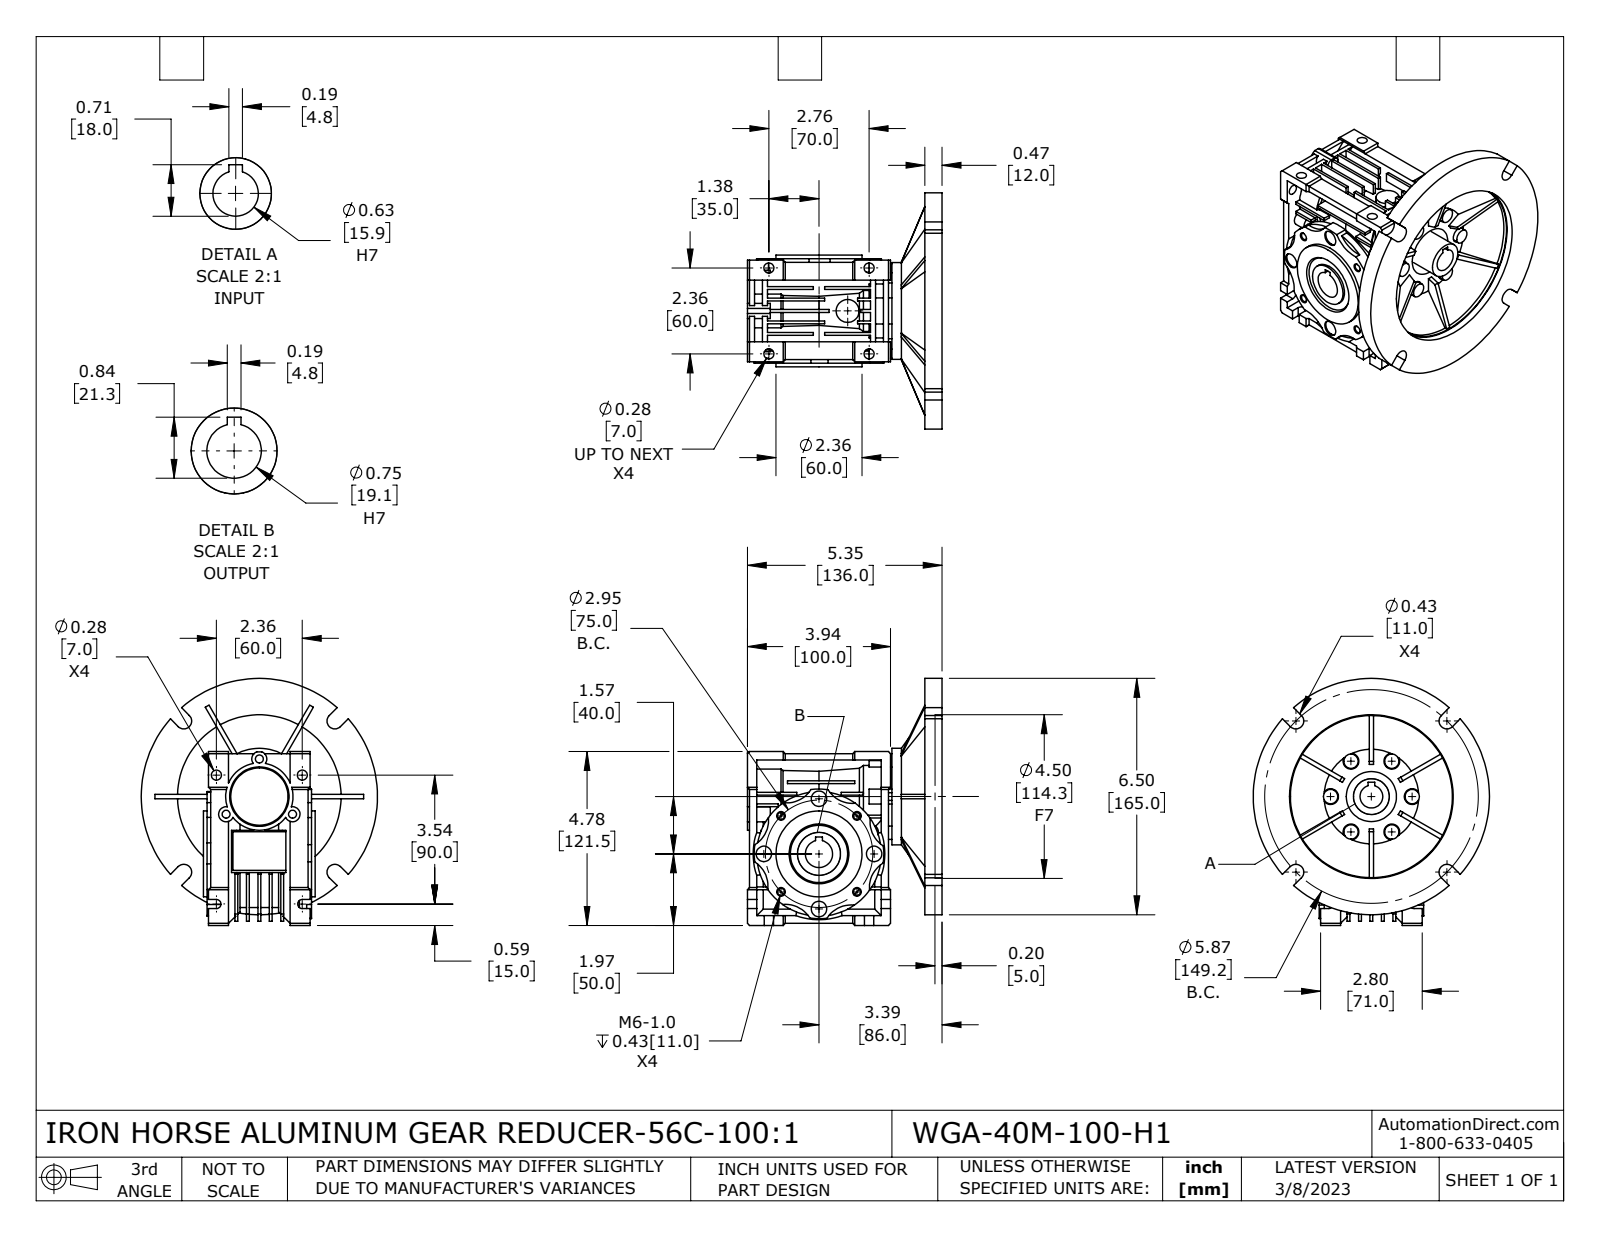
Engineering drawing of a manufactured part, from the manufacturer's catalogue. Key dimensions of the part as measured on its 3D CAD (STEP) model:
Part name (STEP PRODUCT): WGA-40M-100-H1
STEP written by: SolidWorks 2021 (CONFIG_CONTROL_DESIGN)
Units: inches
Bodies: 4 solids, 856 faces (511 planar, 251 cylindrical, 94 other)
Overall size (bounding box): 6.791 × 6.496 × 5.354
Volume: 50.34 in³ · Surface area: 315 in²
Round holes (diameter × count): ⌀0.276 ×6, ⌀0.433 ×6, ⌀0.194 ×4, ⌀0.425 ×4, ⌀0.219 ×3, ⌀0.625 ×1, ⌀0.65 ×1, ⌀0.75 ×1, ⌀0.906 ×1, ⌀1.102 ×1, ⌀1.181 ×1, ⌀1.378 ×1
Round bosses / shafts (diameter × count): ⌀0.394 ×6, ⌀6.496 ×1, ⌀2.953 ×1, ⌀2.657 ×1, ⌀2.362 ×1, ⌀2.126 ×1, ⌀1.85 ×1, ⌀1.417 ×1
Partial cylindrical surfaces — rounded edges, fillets, slot ends (radius × count): R0.787 ×8, R0.126 ×6, R0.206 ×6, R0.217 ×4, R0.207 ×3, R1.713 ×1, R1.716 ×1, R1.781 ×1
Main face-to-face distances: 0.315, 0.472, 0.079, 0.945, 0.236, 0.059, 0.63, 0.098, 0.394, 0.197
Hole centre spacings: 1.122, 1.146, 2.765, 1.943, 1.476, 1.516, 2.088, 2.144
